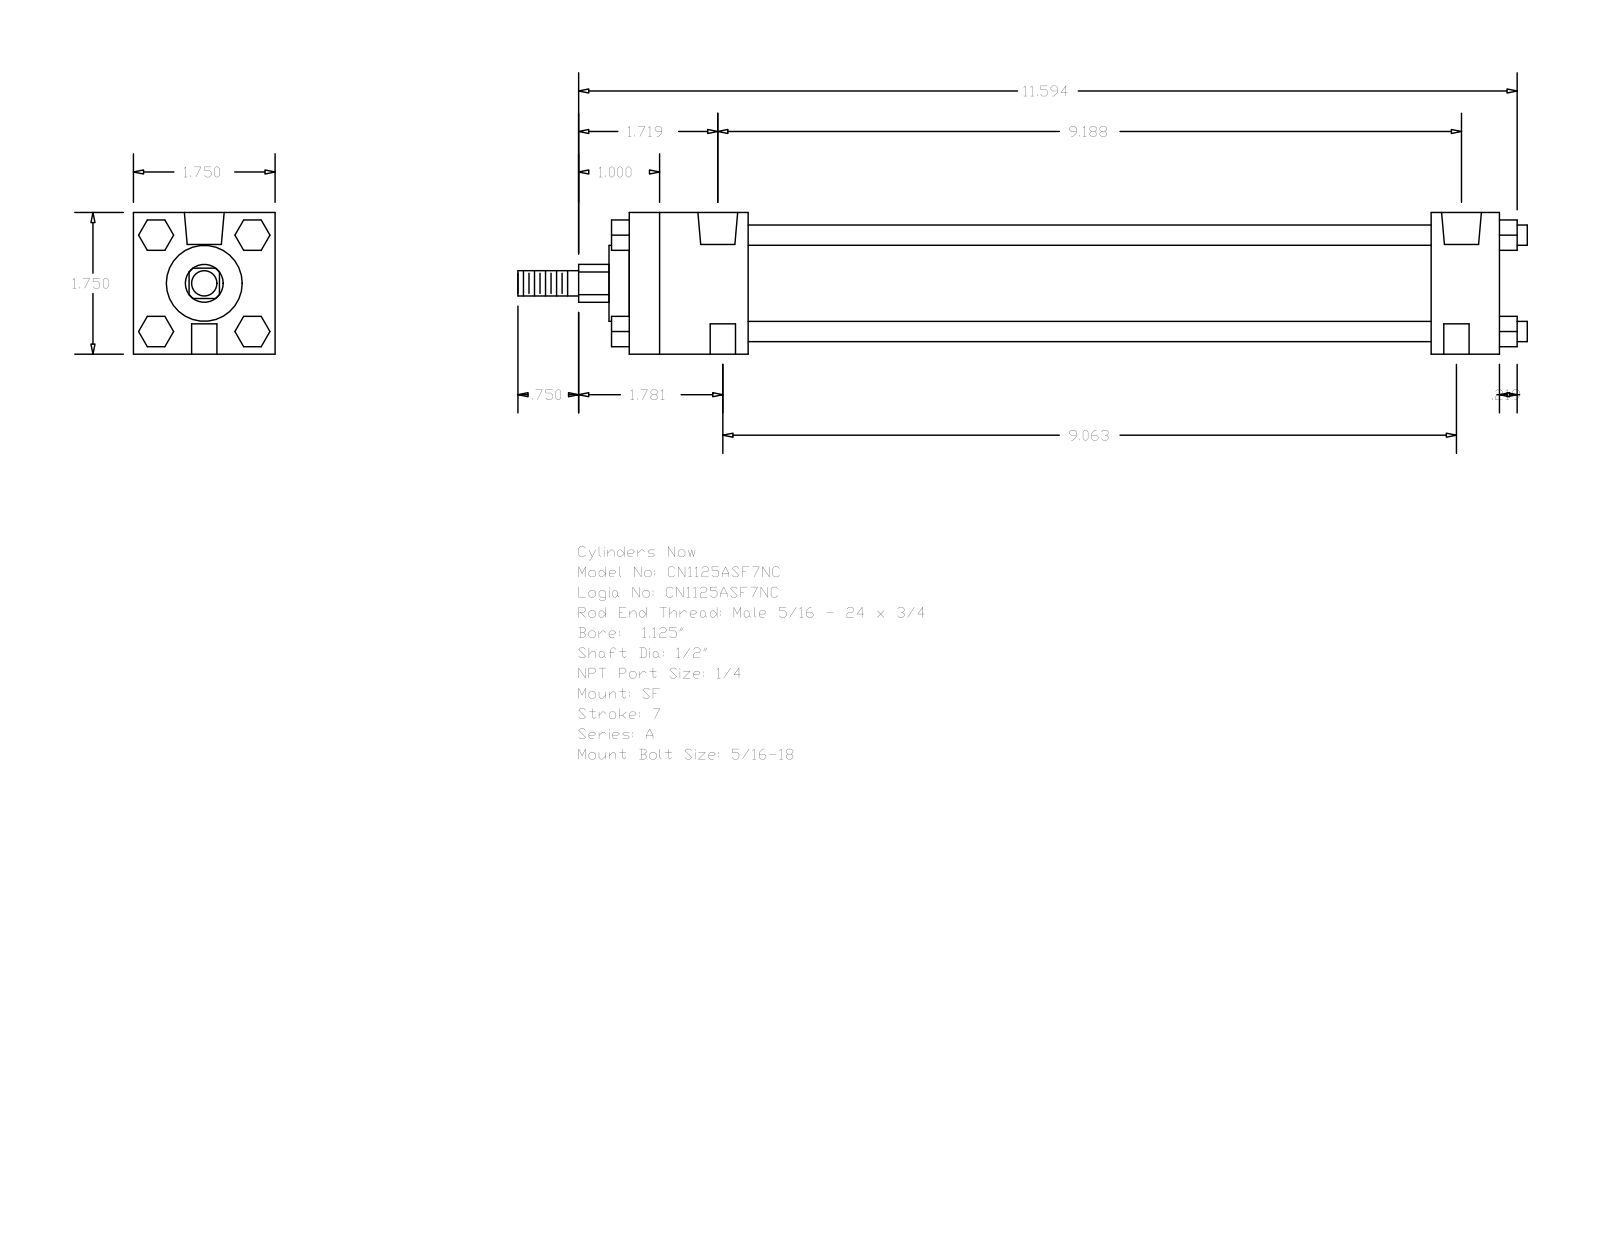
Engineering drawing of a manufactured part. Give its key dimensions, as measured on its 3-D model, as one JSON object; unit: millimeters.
{"part_name": "A_SF__0112_0.5", "step_written_by": "GSSL Pune (CONFIG_CONTROL_DESIGN)", "units": "millimeters", "bodies": {"solids": 0, "faces": 120, "planar": 92, "cylindrical": 28, "other": 0}, "overall_size": [316.71, 44.45, 44.45], "round_holes": [[5.56, 2], [7.94, 2], [12.49, 2]], "round_bosses_or_shafts": [[6.35, 4], [31.88, 1], [23.81, 1], [12.7, 1], [7.94, 1]], "partial_cylinders_radius": [[5.94, 1]], "face_to_face_distances": [44.46, 273.05, 251.61, 21.44, 37.3, 214.31, 235.75, 9.53, 5.59, 26.99], "hole_center_spacings": [230.19, 1.58, 1.59, 231.77, 231.78, 233.36]}
